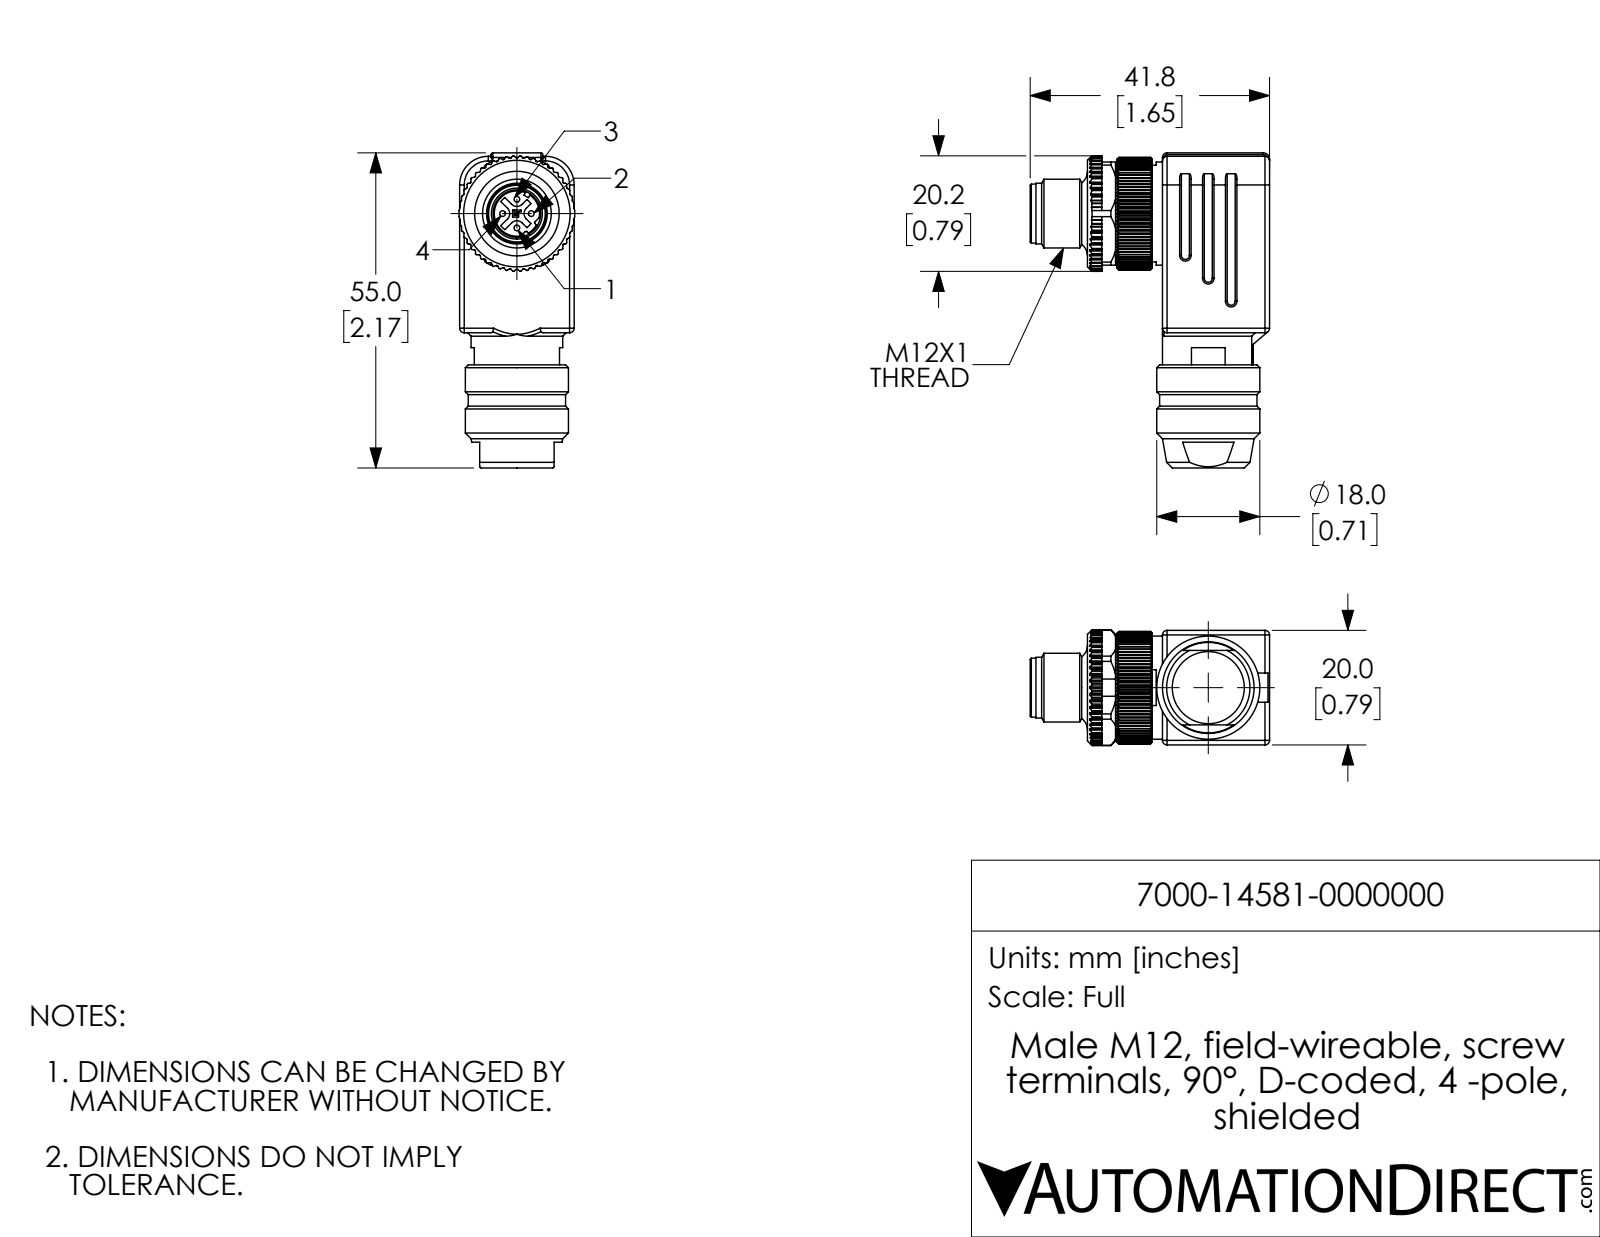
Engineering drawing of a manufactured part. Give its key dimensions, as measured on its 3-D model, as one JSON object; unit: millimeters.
{"part_name": "7000-14581-0000000", "step_written_by": "SolidWorks 2017 (AUTOMOTIVE_DESIGN)", "units": "millimeters", "bodies": {"solids": 1, "faces": 999, "planar": 419, "cylindrical": 319, "other": 261}, "overall_size": [55, 41.8, 20.2], "volume_mm3": 20760, "surface_area_mm2": 6877, "round_holes": [[8.3, 1], [9.6, 1]], "round_bosses_or_shafts": [[1, 4], [18, 2], [17, 1], [16, 1], [15, 1], [12, 1], [10.6, 1], [10.3, 1]], "partial_cylinders_radius": [[0.2, 105], [0.3, 18], [0.8, 11], [1.3, 4], [1, 3], [5, 2], [1.1, 1], [3, 1]], "face_to_face_distances": [20, 18.7, 19.6, 13.4, 0.4, 55, 13.4, 26.6, 7.9, 31.8]}
